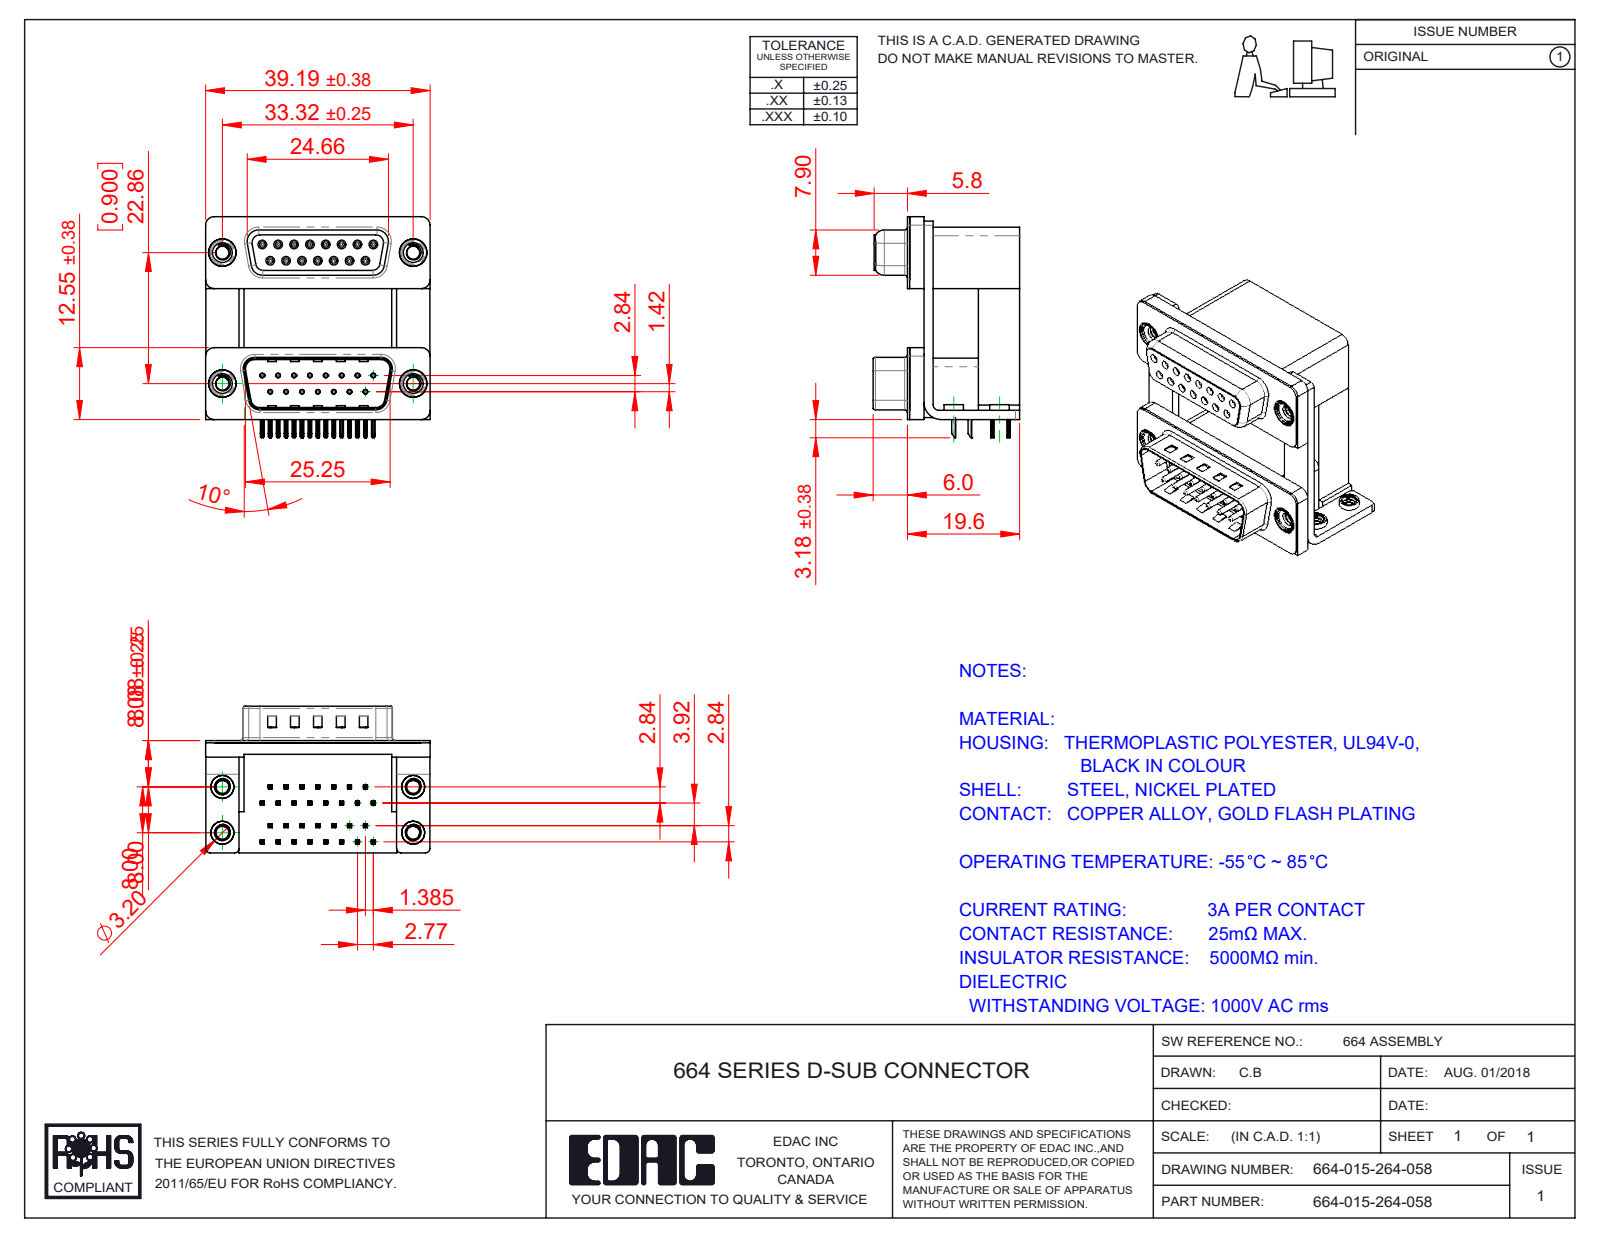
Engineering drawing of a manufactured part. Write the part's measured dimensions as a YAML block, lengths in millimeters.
part_name: "664 4-40 Threaded Board Mount; 664 Contact Top Upper_H; 664 Housing Lower_15 Contacts; 664 Shell Receptacle_15 Contacts (+8 more)"
step_written_by: "SolidWorks 2020 (CONFIG_CONTROL_DESIGN)"
units: millimeters
bodies: {solids: 45, faces: 4052, planar: 2027, cylindrical: 1090, other: 935}
overall_size: [39.19, 38.59, 25.6]
volume: 15977
surface_area: 17807
round_holes:
  - {diameter: 0.8, count: 30}
  - {diameter: 0.35, count: 15}
  - {diameter: 0.9, count: 15}
  - {diameter: 2.26, count: 8}
  - {diameter: 2.75, count: 4}
  - {diameter: 3.2, count: 4}
  - {diameter: 3.5, count: 4}
  - {diameter: 4, count: 4}
  - {diameter: 4.8, count: 4}
  - {diameter: 5, count: 4}
round_bosses_or_shafts:
  - {diameter: 1.2, count: 15}
  - {diameter: 0.75, count: 15}
  - {diameter: 4.9, count: 4}
  - {diameter: 4.75, count: 4}
  - {diameter: 4, count: 4}
  - {diameter: 3.9, count: 4}
  - {diameter: 3.4, count: 4}
partial_cylinders:
  - {radius: 0.1, count: 120}
  - {radius: 0.15, count: 60}
  - {radius: 0.25, count: 60}
  - {radius: 0.12, count: 30}
  - {radius: 0.35, count: 30}
  - {radius: 1.5, count: 16}
  - {radius: 0.34, count: 15}
  - {radius: 0.5, count: 12}
face_to_face_distances: [0.4, 19.2, 12, 7.2, 16.7, 9.5, 2.5, 2.19, 22.86, 12.4]
hole_center_spacings: [3.16, 2.77, 23.03, 5.54, 23.52, 8.31, 22.86, 24.32]
